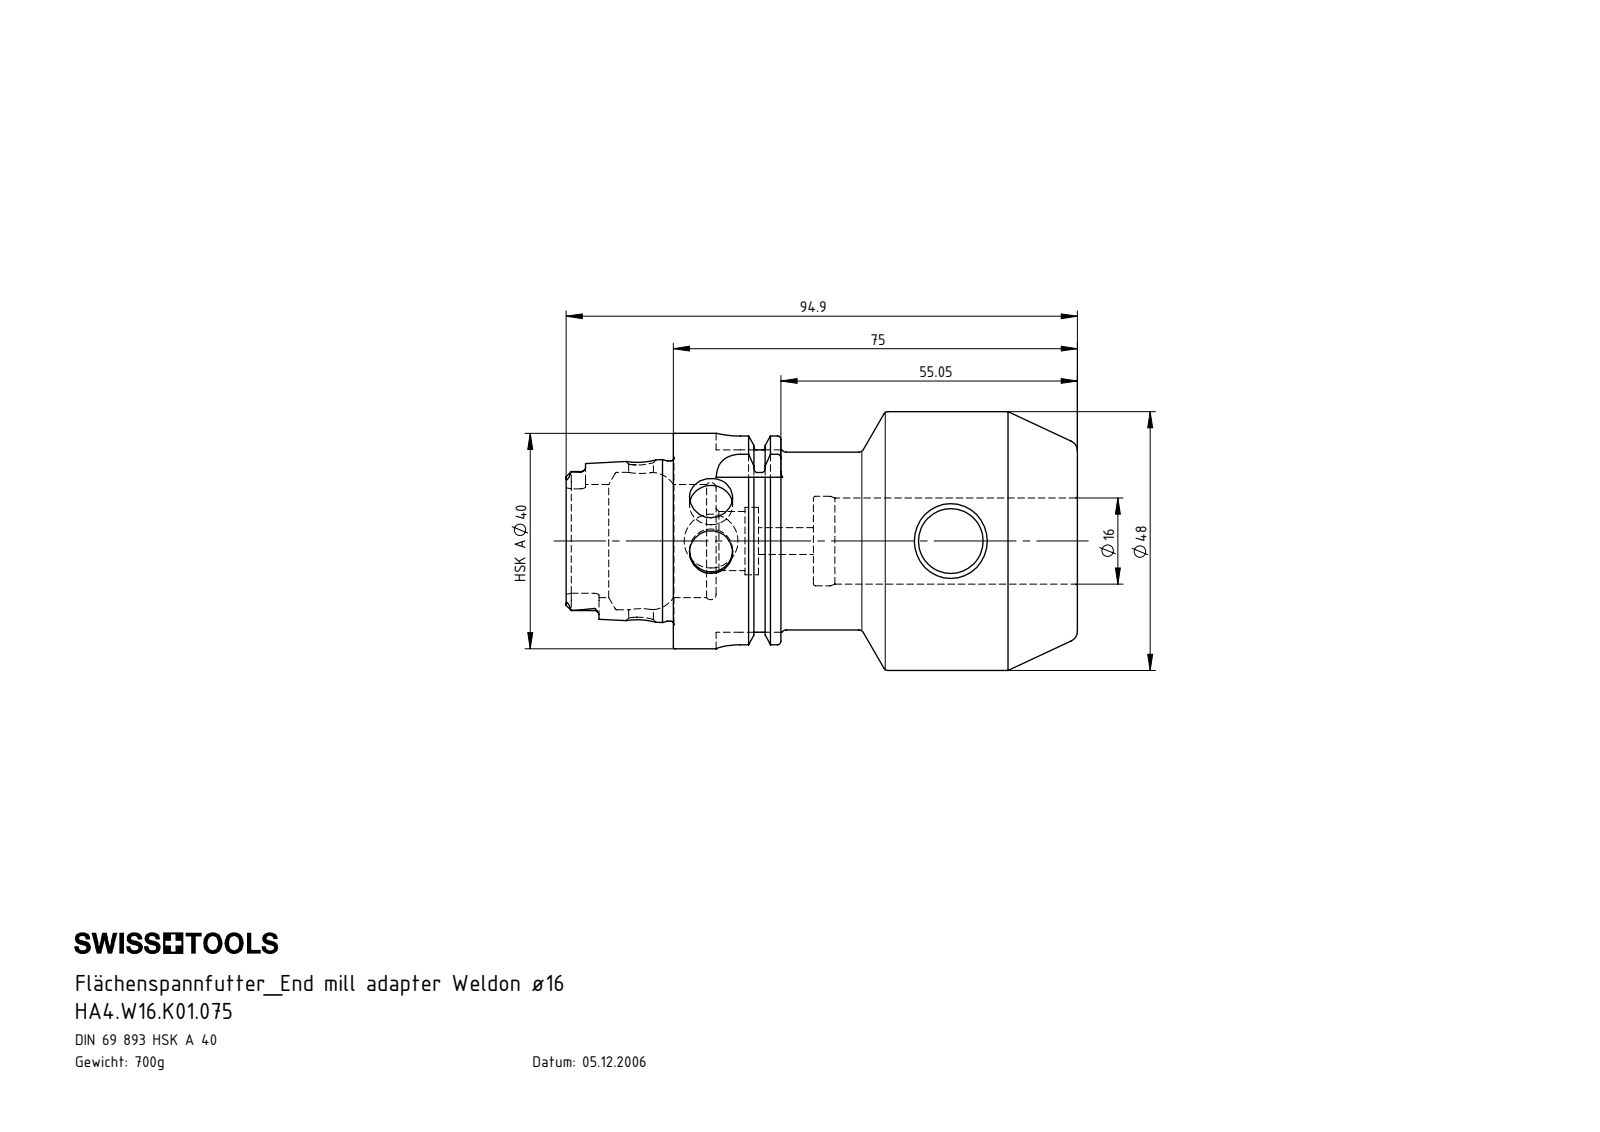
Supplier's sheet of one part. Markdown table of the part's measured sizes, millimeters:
| quantity | value |
| --- | --- |
| part name | W16-ER1.001.016; HA4-W16.K01.075_B_Fertigbearbeitung; HA4.W16.K01.075 |
| STEP written by | SolidWorks 2017 (CONFIG_CONTROL_DESIGN) |
| units | millimeters |
| bodies | 2 solids, 207 faces (58 planar, 60 cylindrical, 89 other) |
| overall size | 94.9 × 48 × 48 |
| volume | 91 277 mm³ |
| surface area | 21 916 mm² |
| round holes (diameter × count) | 8 × 2, 4.6 × 1, 5 × 1, 10 × 1, 11 × 1, 12 × 1, 12.5 × 1, 16 × 1, 16.6 × 1, 21 × 1, 25.5 × 1 |
| round bosses / shafts (diameter × count) | 48 × 1, 40 × 1, 34.75 × 1, 33 × 1, 29.71 × 1, 14 × 1 |
| partial cylindrical surfaces (radius × count) | 0.9 × 6, 1.88 × 4, 4.5 × 4 |
| main face-to-face distances | 75, 7.95, 67.05, 26, 18.05, 49, 19.95, 12, 6.05, 55.05 |
| hole center spacings | 44.5 |
